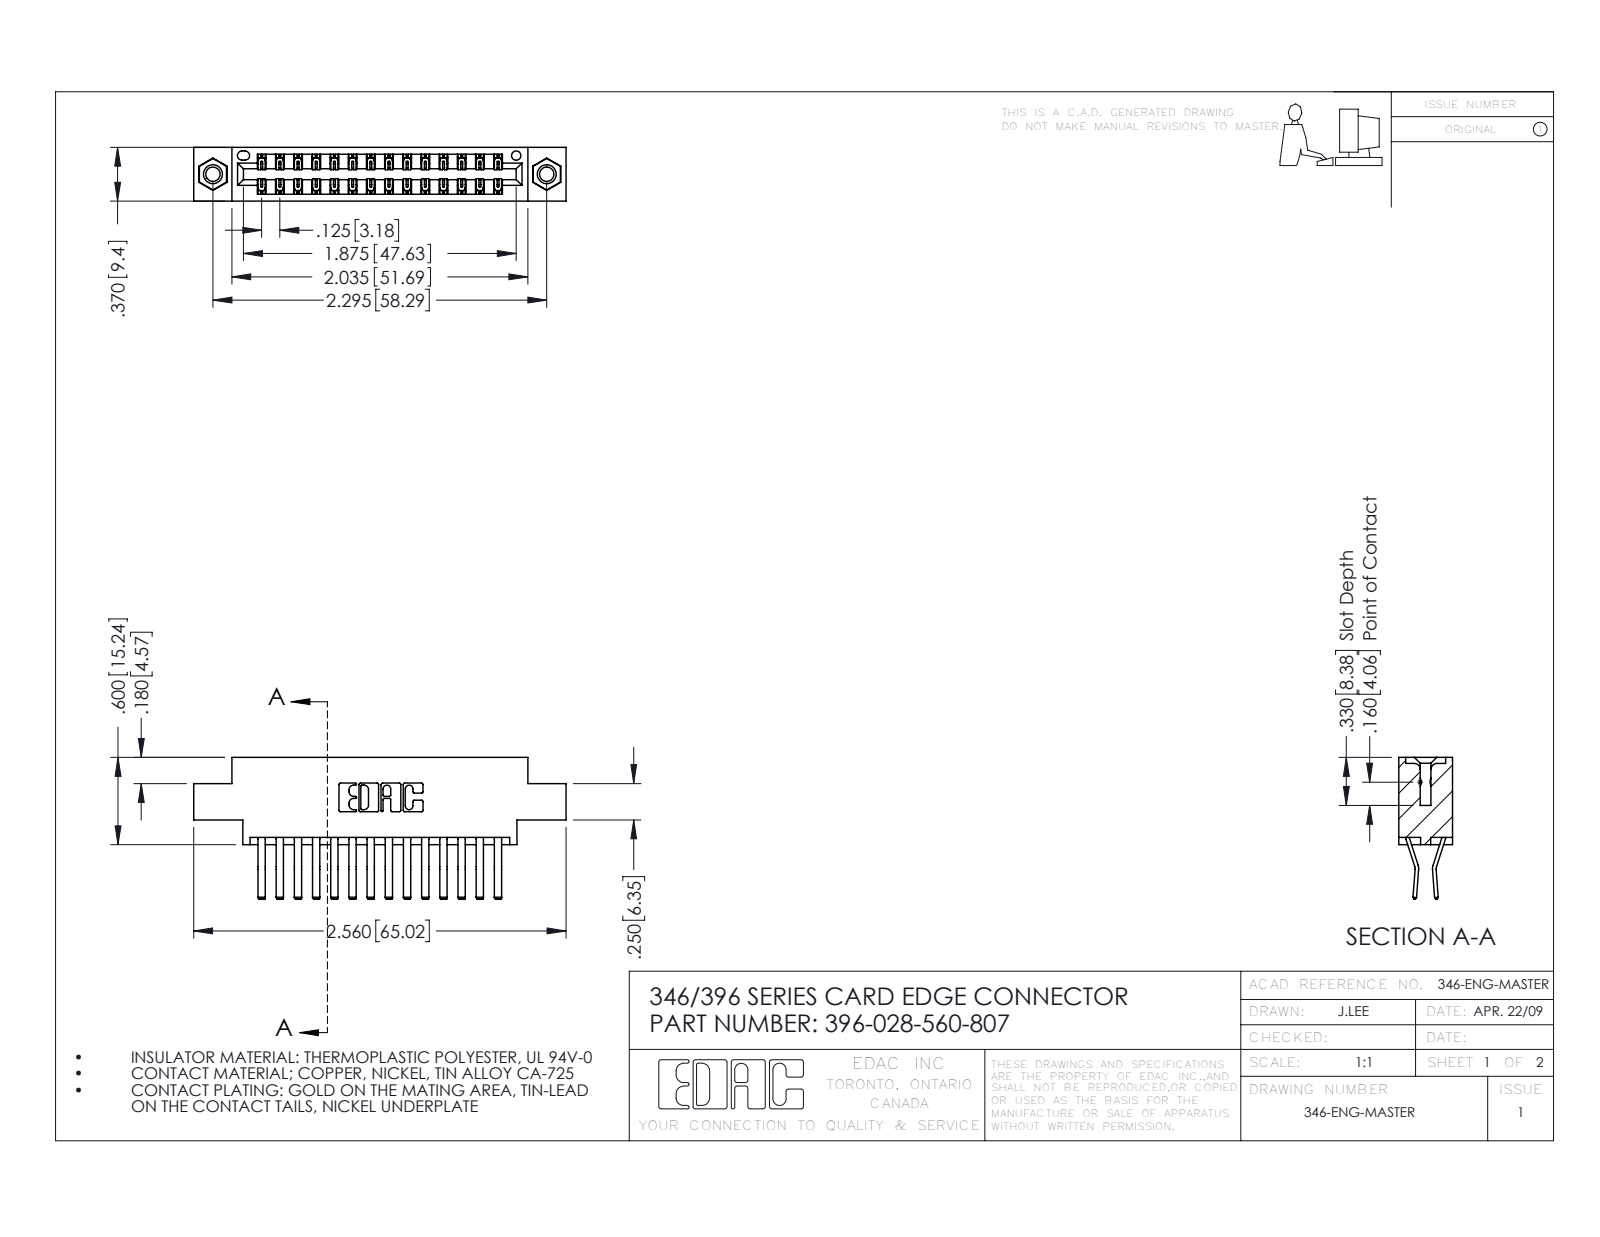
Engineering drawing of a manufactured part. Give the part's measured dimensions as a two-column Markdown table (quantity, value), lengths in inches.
| quantity | value |
| --- | --- |
| part name | 346 Part_0.170 Offset - 0.156 Dia-TI; 396-028-560-807; 345-292-001_560 Tail; 345-250-001_345-250-005-103 |
| STEP written by | SolidWorks 2016 (CONFIG_CONTROL_DESIGN) |
| units | inches |
| bodies | 31 solids, 1698 faces (1092 planar, 590 cylindrical, 16 other) |
| overall size | 2.56 × 0.975 × 0.37 |
| volume | 0.375 in³ |
| surface area | 13.49 in² |
| round holes (diameter × count) | 0.098 × 2, 0.125 × 2, 0.156 × 2, 0.064 × 1 |
| round bosses / shafts (diameter × count) | 0.155 × 2 |
| partial cylindrical surfaces (radius × count) | 0.006 × 42, 0.01 × 22, 0.007 × 6, 0.031 × 6, 0.026 × 3, 0.01 × 2, 0.014 × 2, 0.022 × 2 |
| main face-to-face distances | 0.048, 0.322, 0.37, 0.25, 0.025, 0.072, 0.298, 0.222, 0.148, 0.275 |
| hole center spacings | 0.246, 2.089, 2.295 |
